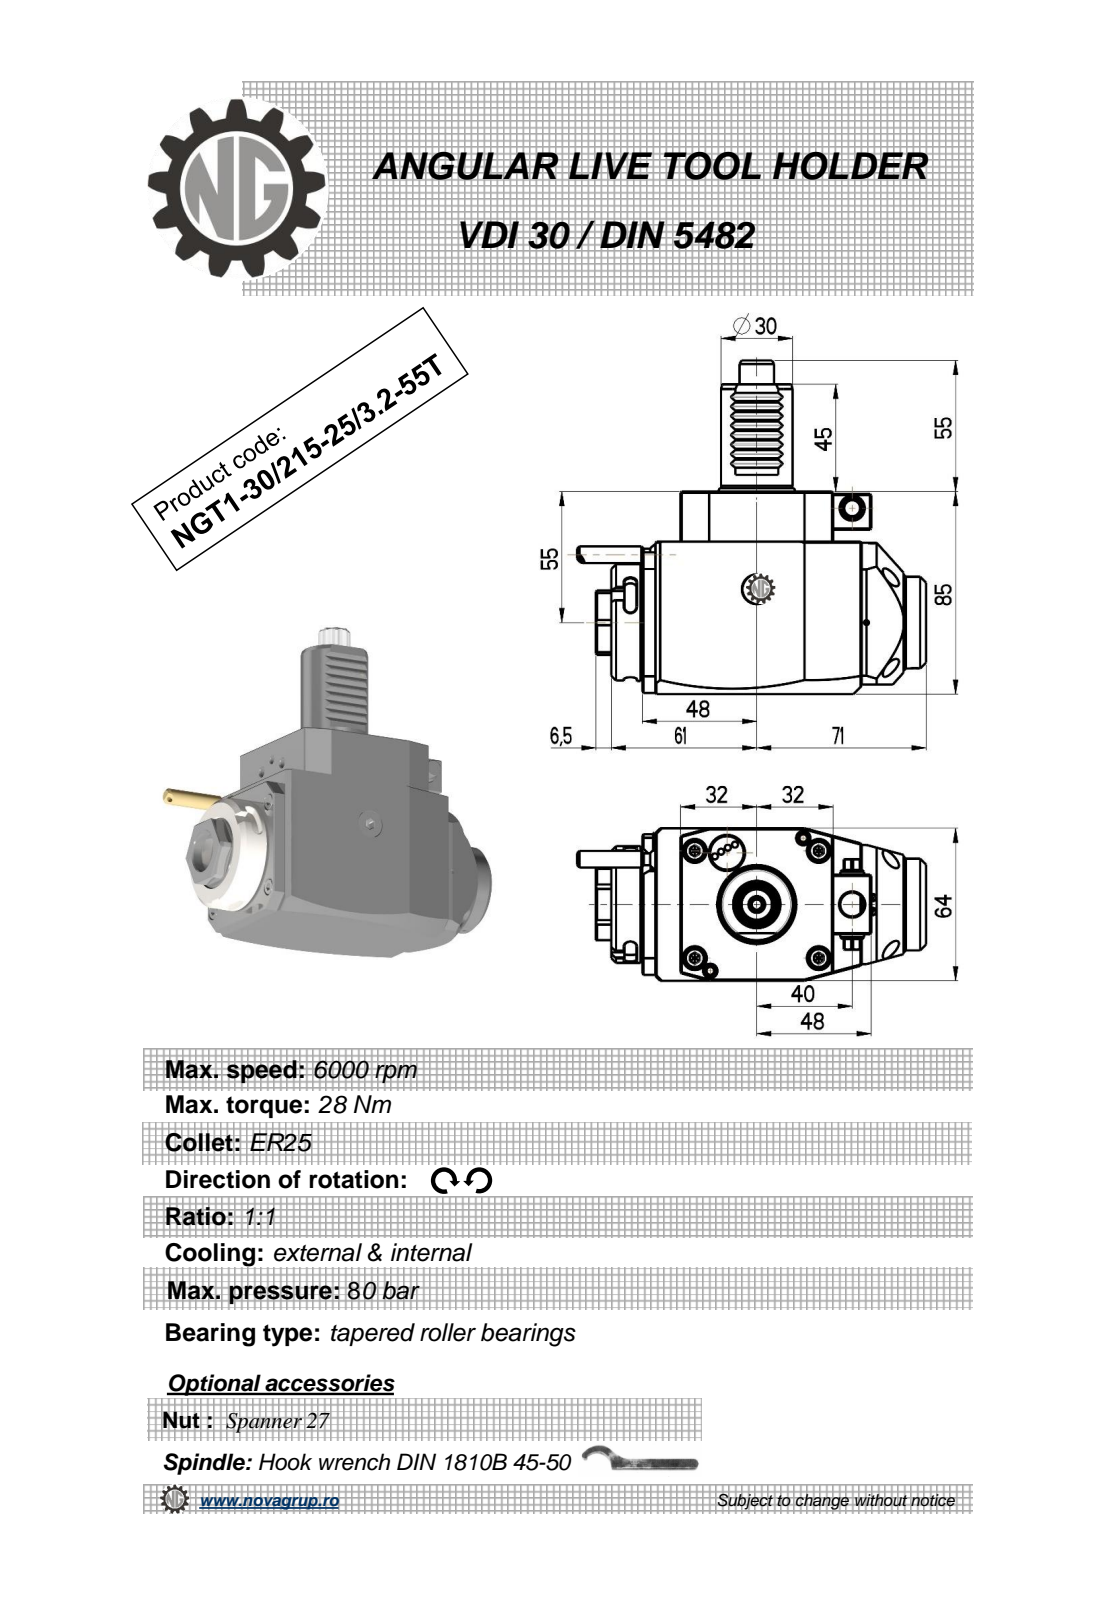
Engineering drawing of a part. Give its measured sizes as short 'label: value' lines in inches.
name: NGT1_30_215_25_3_2_55T
written by: PRO/ENGINEER BY PARAMETRIC TECHNOLOGY CORPORATION, 2010280 (CONFIG_CONTROL_DESIGN)
unit: in
bodies: 1 solid, 378 faces (176 planar, 114 cylindrical, 88 other)
size: 5.763 × 5.512 × 2.52
volume: 34.1 in³; area: 77.52 in²
holes: 1× ⌀0.098, 1× ⌀0.118, 1× ⌀0.165, 1× ⌀0.209, 1× ⌀0.335, 1× ⌀0.374, 1× ⌀0.394, 1× ⌀0.709
bosses: 2× ⌀0.315, 1× ⌀1.929, 1× ⌀1.654, 1× ⌀1.516, 1× ⌀1.181, 1× ⌀0.394, 1× ⌀0.276, 1× ⌀0.197
rounds: 16× R0.115, 8× R0.012, 6× R0.098, 2× R7.087, 1× R0.152, 1× R0.177, 1× R0.226, 1× R0.285
face distances: 2.52, 3.346, 0.63, 3.15, 0.512, 0.827, 1.142, 5.197, 4.685, 4.055
hole spacings: 1.03, 1.348, 1.575, 1.831
